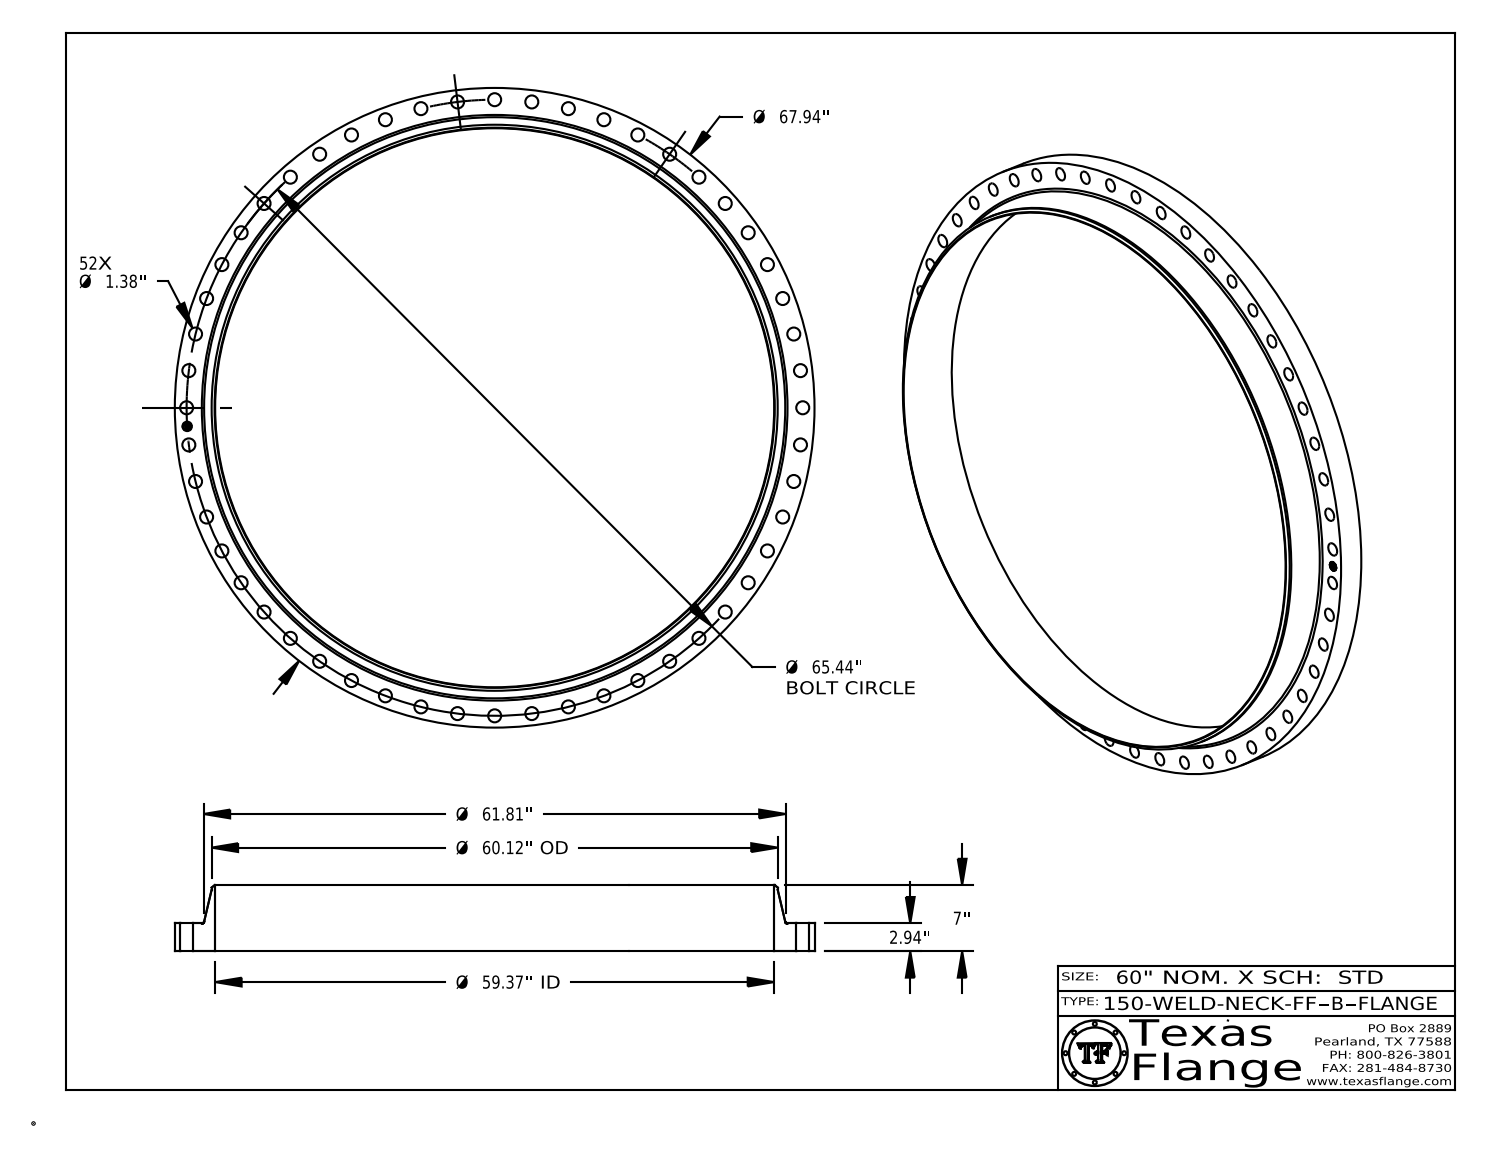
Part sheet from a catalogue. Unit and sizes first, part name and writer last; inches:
Units: inches
Overall size (bounding box): 67.94 × 67.94 × 7
Round holes (diameter × count): ⌀1.38 ×52, ⌀1 ×1, ⌀59.37 ×1
Round bosses / shafts (diameter × count): ⌀0.061 ×8, ⌀67.94 ×1, ⌀60.12 ×1, ⌀0.788 ×1
Main face-to-face distances: 2.94, 7, 4.06, 0.015, 2.925, 4.075, 0.298, 0.293, 0.019, 0.054
Hole centre spacings: 32.72, 64.368, 65.32, 61.187, 63.539, 64.963, 3.951, 7.888
Volume: 2 860 in³ · Surface area: 4 746 in²
Bodies: 1 solid, 504 faces (368 planar, 130 cylindrical, 6 other)
Part name (STEP PRODUCT): 150-WELD-NECK-FF, Series B
STEP written by: CATIA V5 STEP AP214 (AUTOMOTIVE_DESIGN)
